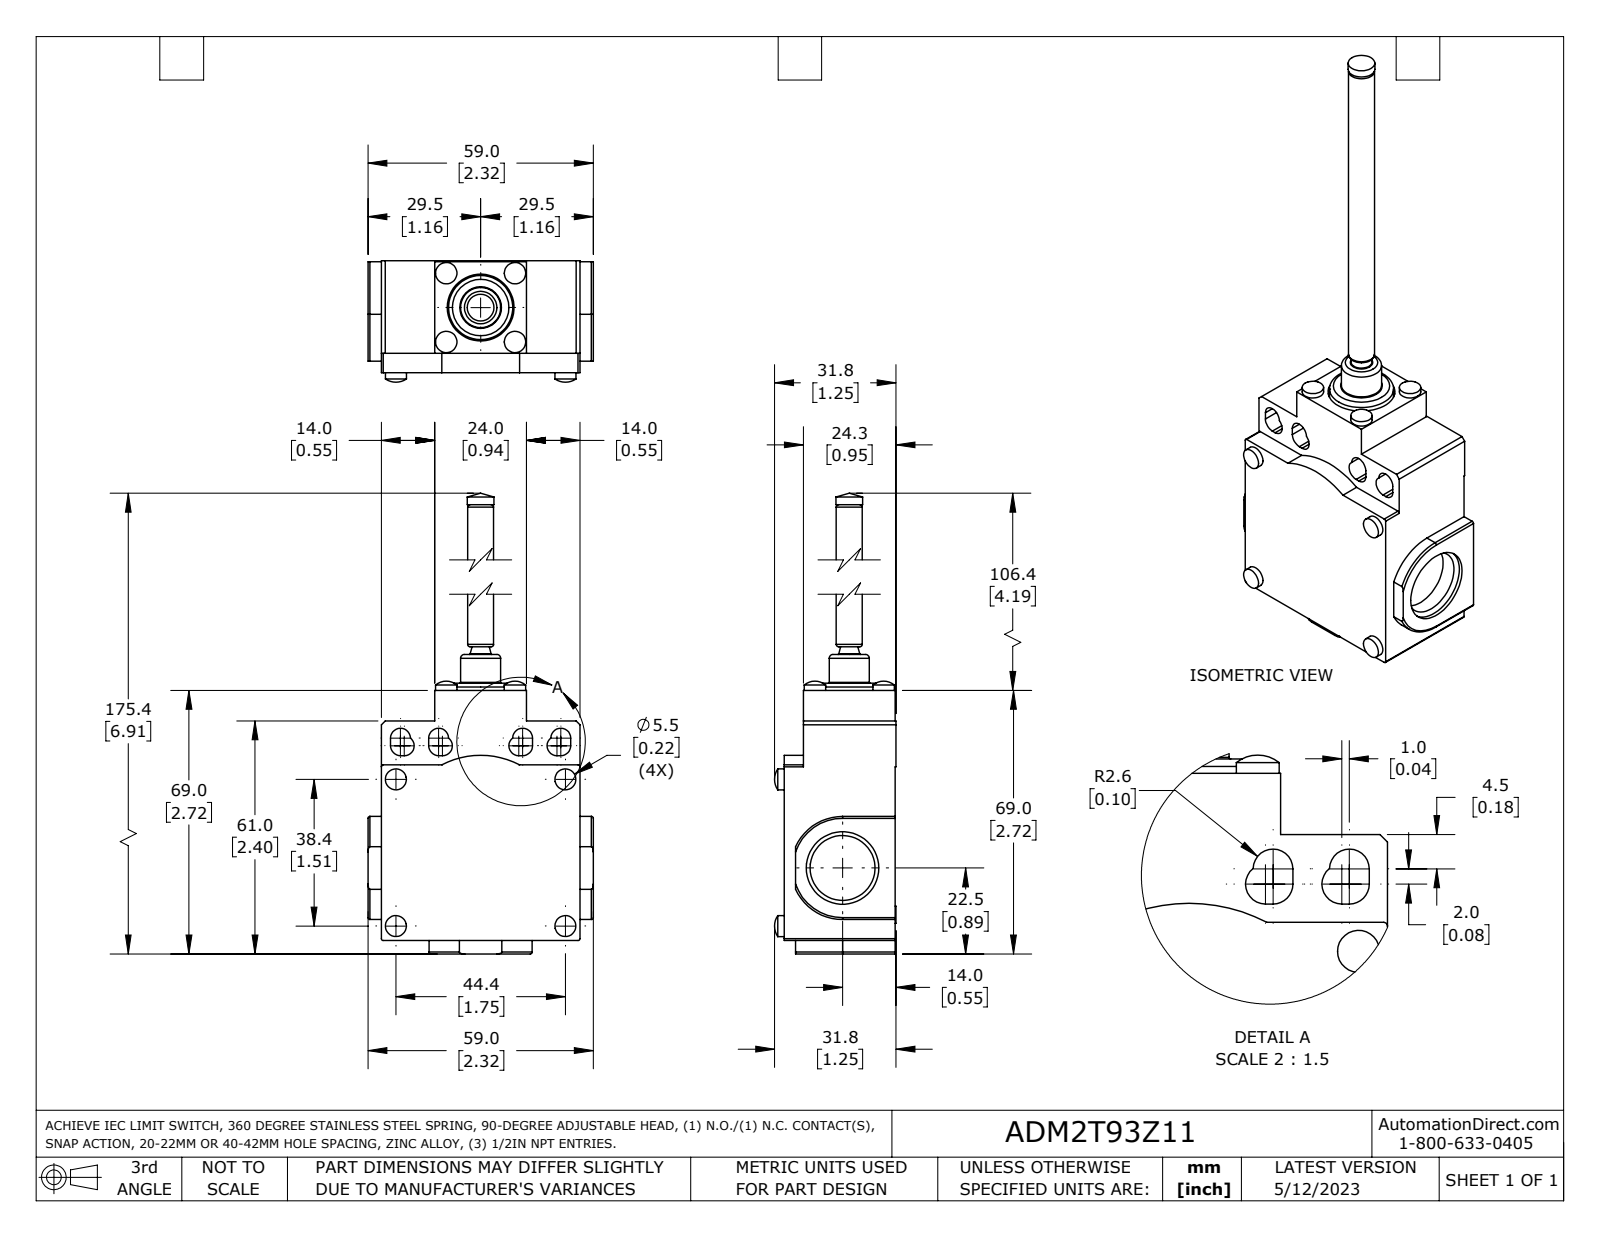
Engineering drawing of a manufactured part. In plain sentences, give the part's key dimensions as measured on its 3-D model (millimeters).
The part is named "ADM2T93Z11". Its 3-D file was written by "SolidWorks 2021 (AUTOMOTIVE_DESIGN)". It is 1 solid with 147 faces: 66 planar, 56 cylindrical and 25 other. Overall it measures 175.4 by 59 by 31.8 millimeters. Its volume is 92 690 cubic millimeters and its surface area 19 550 square millimeters. Round holes: 2 of diameter 17, 2 of diameter 19, 1 of diameter 17.5. Round bosses or shafts: 4 of diameter 5.6, 4 of diameter 5.5, 1 of diameter 16.8, 1 of diameter 10.5, 1 of diameter 7, 1 of diameter 6.8. Partial cylindrical surfaces (rounded edges, fillets, slot ends): 12 of radius 2.6, 10 of radius 0.5, 2 of radius 13.5, 1 of radius 10, 1 of radius 10.2, 1 of radius 22. The main face-to-face distances are 29.1, 3.5, 52, 24, 6, 2.5, 29.3, 55.5, 57.5, 24.3. The hole center spacings are 1.8.
